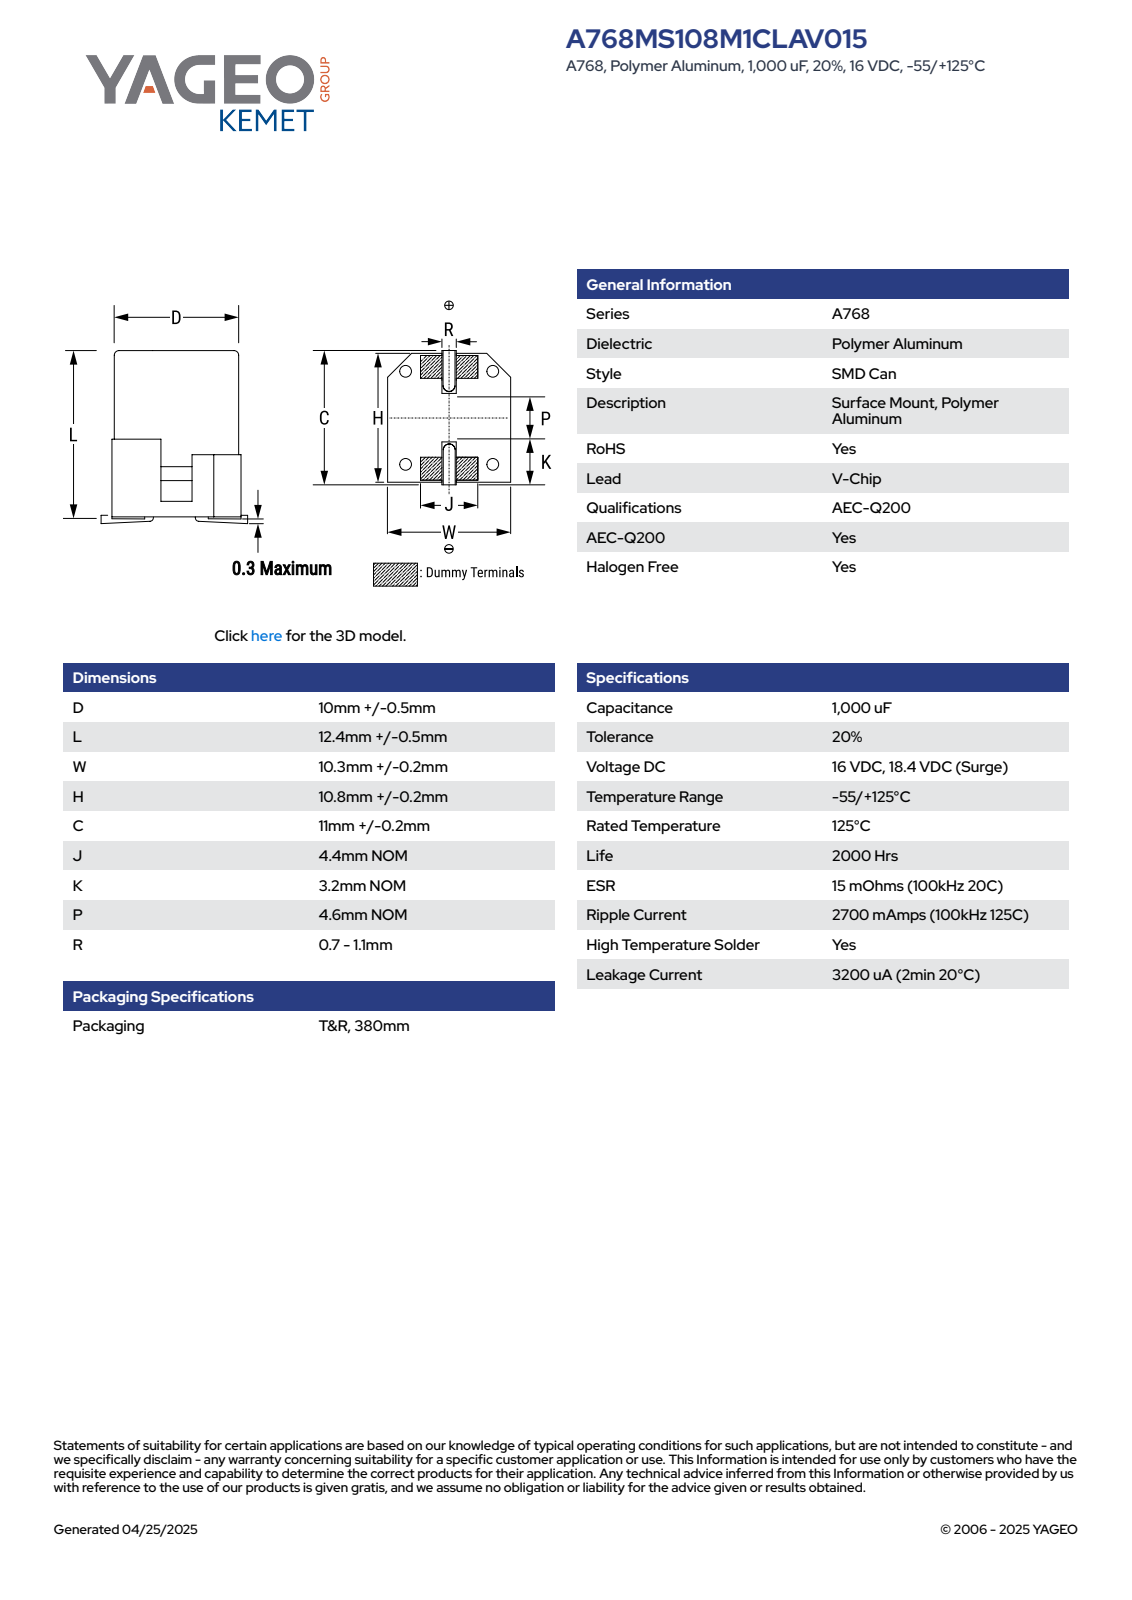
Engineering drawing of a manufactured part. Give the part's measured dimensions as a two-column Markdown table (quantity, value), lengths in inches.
| quantity | value |
| --- | --- |
| part name | CAC_KAV_10X12.4_D10.5L12.9W1.1F0.2A10.5B11C11.2P3.2 |
| STEP written by | SolidWorks 2014 (AUTOMOTIVE_DESIGN) |
| units | inches |
| bodies | 5 solids, 76 faces (59 planar, 11 cylindrical, 6 other) |
| overall size | 0.508 × 0.441 × 0.413 |
| volume | 0.067 in³ |
| surface area | 1.54 in² |
| round bosses / shafts (diameter × count) | 0.395 × 1 |
| partial cylindrical surfaces (radius × count) | 0.008 × 2, 0.164 × 1, 0.207 × 1 |
| main face-to-face distances | 0.041, 0.5, 0.459, 0.5, 0.46, 0.413, 0.433, 0.203, 0.163, 0.297 |
